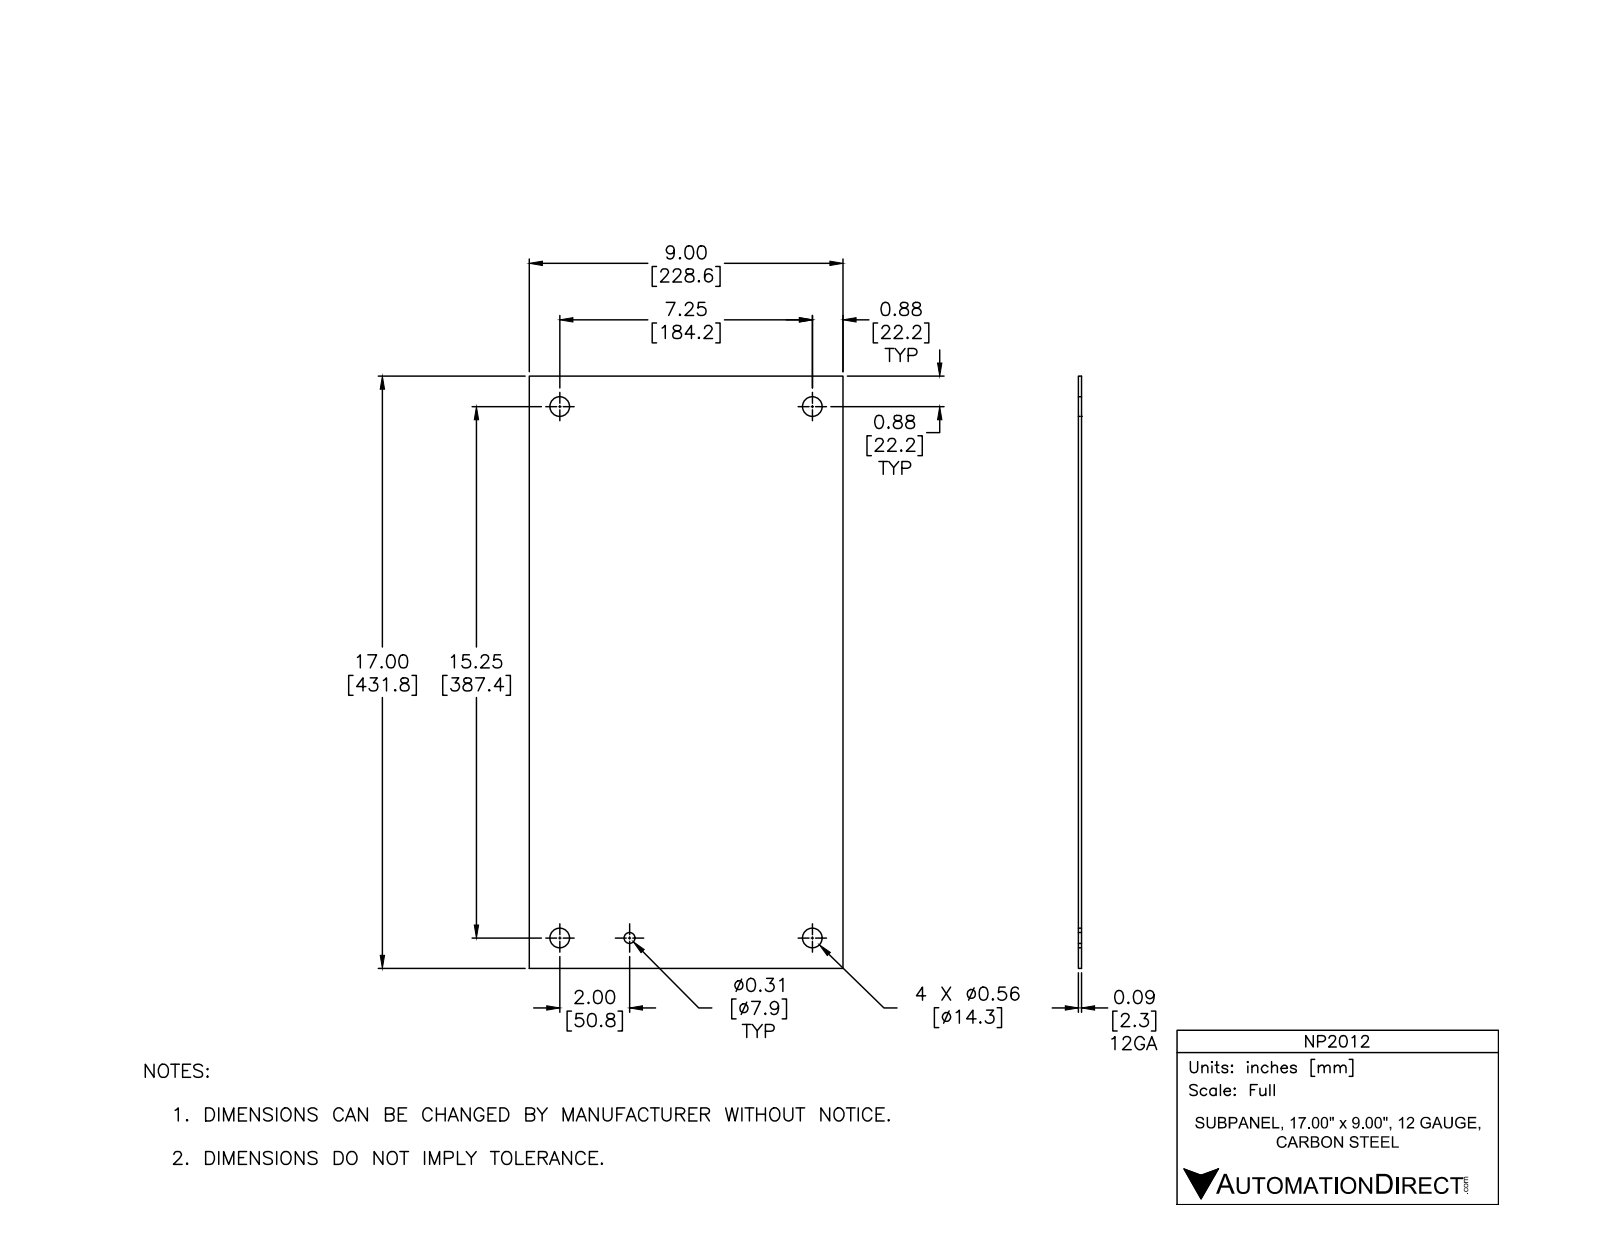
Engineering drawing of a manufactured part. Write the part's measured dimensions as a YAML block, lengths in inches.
part_name: "NP2012"
step_written_by: "Autodesk Inventor 2012 (AUTOMOTIVE_DESIGN)"
units: inches
bodies: {solids: 1, faces: 11, planar: 6, cylindrical: 5, other: 0}
overall_size: [17, 9, 0.094]
volume: 14.24
surface_area: 309.5
round_holes:
  - {diameter: 0.563, count: 4}
  - {diameter: 0.31, count: 1}
face_to_face_distances: [0.094, 9, 17]
hole_center_spacings: [7.25, 16.886, 2, 5.25, 15.25, 15.25, 15.381, 16.128]
